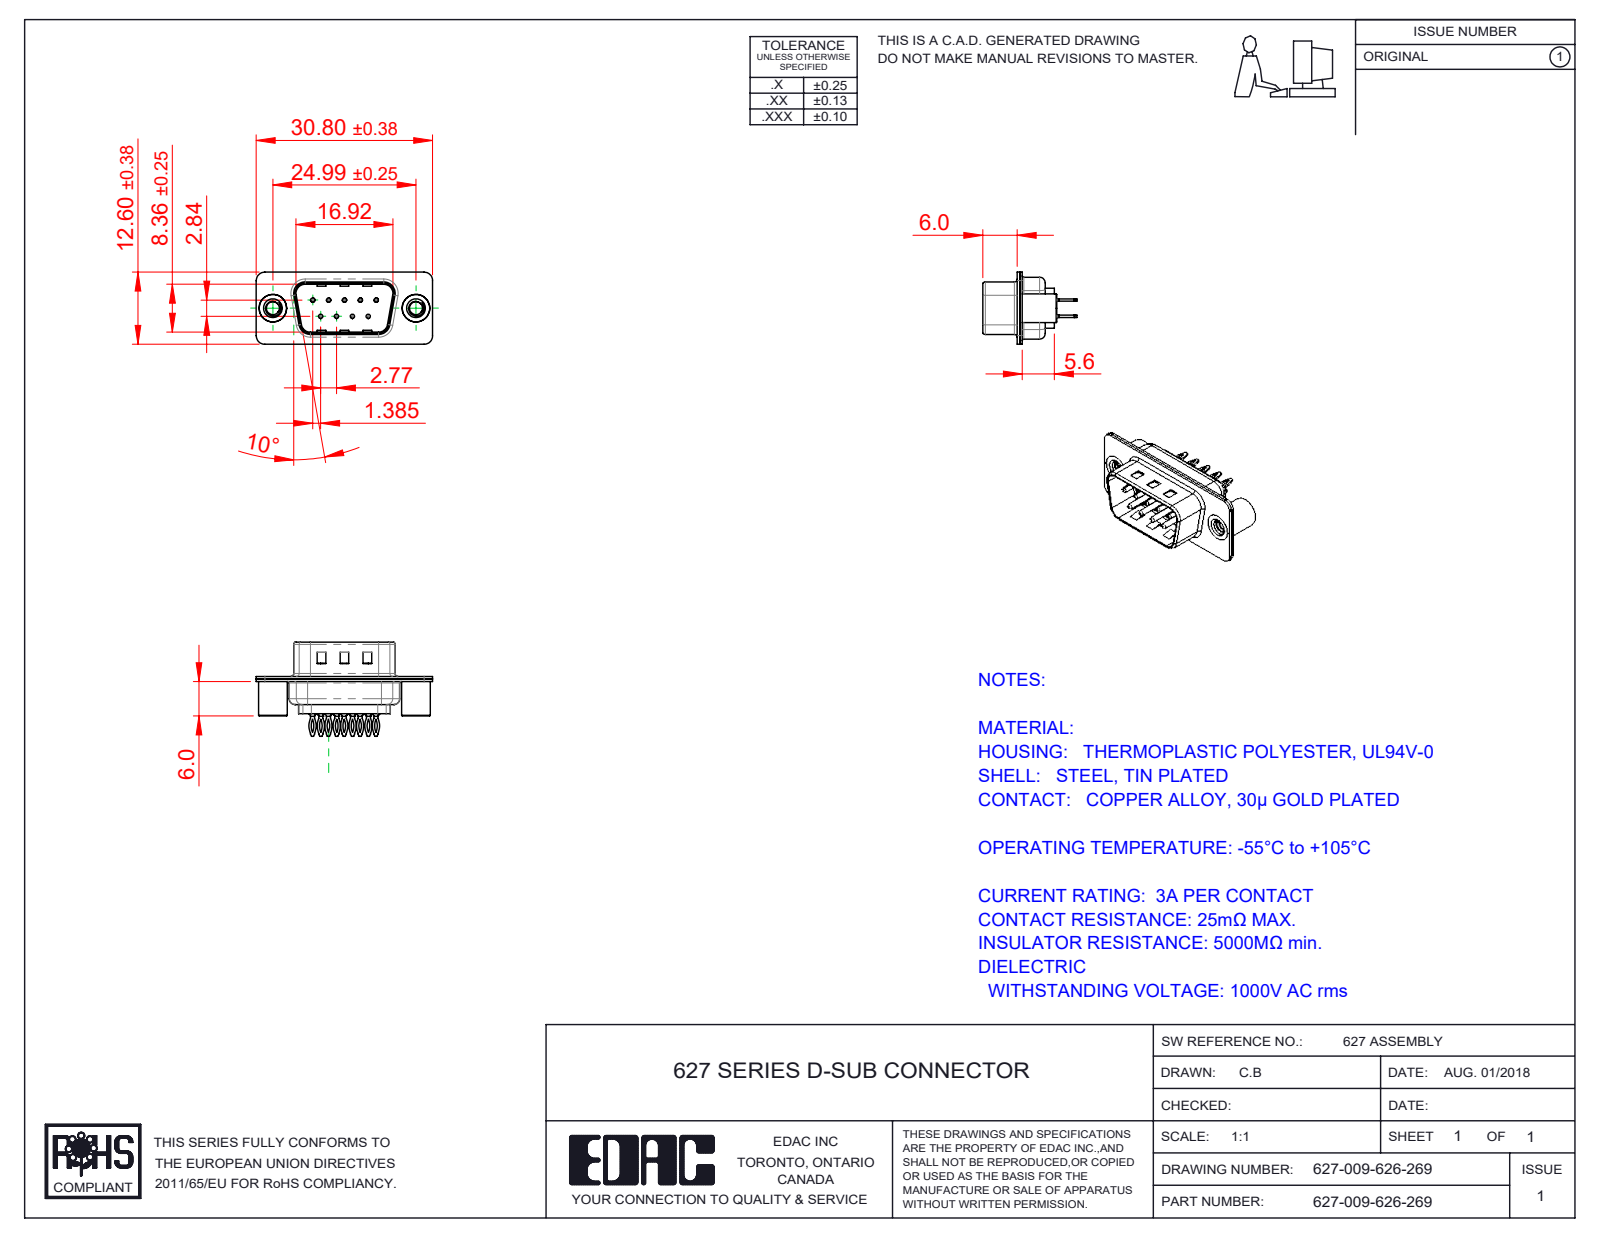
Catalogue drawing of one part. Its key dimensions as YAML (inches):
part_name: "627 4-40 Threaded Standoff BS; 627 Shell Rear_09 Contacts; 627-009-626-269; 627 Contact Row 2_26L (+3 more)"
step_written_by: "SolidWorks 2020 (CONFIG_CONTROL_DESIGN)"
units: inches
bodies: {solids: 14, faces: 1010, planar: 287, cylindrical: 428, other: 295}
overall_size: [1.213, 0.648, 0.496]
volume: 0.086
surface_area: 6.349
round_holes:
  - {diameter: 0.014, count: 9}
  - {diameter: 0.043, count: 9}
  - {diameter: 0.063, count: 9}
  - {diameter: 0.089, count: 2}
  - {diameter: 0.157, count: 2}
  - {diameter: 0.189, count: 2}
round_bosses_or_shafts:
  - {diameter: 0.079, count: 9}
  - {diameter: 0.059, count: 9}
  - {diameter: 0.03, count: 9}
  - {diameter: 0.197, count: 2}
  - {diameter: 0.193, count: 2}
partial_cylinders:
  - {radius: 0.059, count: 18}
  - {radius: 0.115, count: 18}
  - {radius: 0.131, count: 18}
  - {radius: 0.079, count: 12}
  - {radius: 0.02, count: 8}
  - {radius: 0.063, count: 8}
  - {radius: 0.01, count: 4}
  - {radius: 0.024, count: 4}
face_to_face_distances: [0.016, 0.018, 0.035, 0.032, 0.377, 0.055, 0.345, 0.256, 0.02, 0.059]
hole_center_spacings: [0.124, 0.109, 0.218, 0.198, 0.198, 0.327, 0.294, 0.295]
